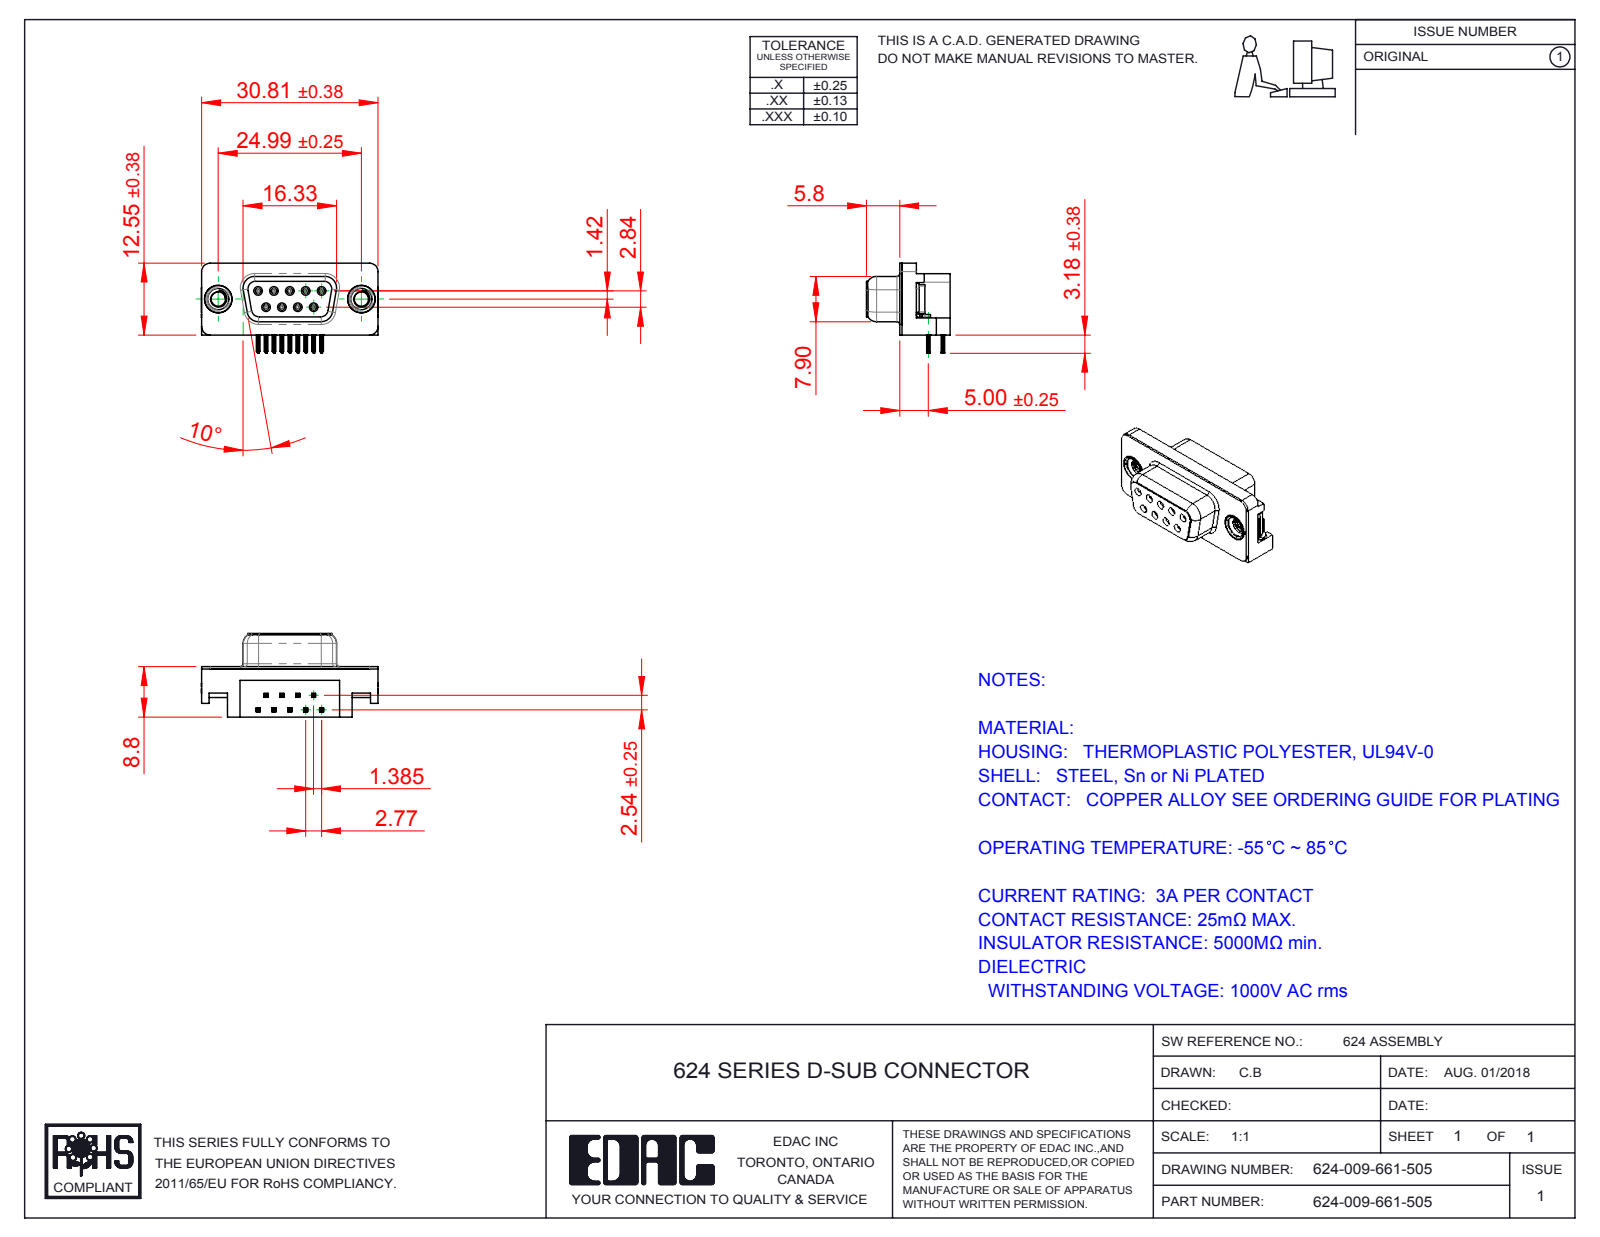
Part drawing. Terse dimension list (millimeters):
name: 624 Shell_9 Socket; 624 Housing_9 Socket; 624-009-661-505; 624 M3 Threaded Rivet (+3 more)
written by: SolidWorks 2016 (CONFIG_CONTROL_DESIGN)
unit: mm
bodies: 15 solids, 1520 faces (642 planar, 410 cylindrical, 468 other)
size: 30.89 × 15.73 × 14.6
volume: 2 932 mm³; area: 4 338 mm²
holes: 9× ⌀0.8, 9× ⌀0.9, 2× ⌀2.5, 2× ⌀4, 2× ⌀4.8, 2× ⌀5
bosses: 9× ⌀1.2, 2× ⌀4.9, 2× ⌀4.75, 2× ⌀3.9
rounds: 72× R0.1, 36× R0.15, 18× R0.35, 18× R1, 9× R0.34, 8× R0.25, 8× R1.35, 7× R1.5
face distances: 0.4, 8.4, 8.8, 2.9, 2.5, 6.2, 5.9, 0.35, 10.69, 10.34
hole spacings: 3.16, 2.77, 5.54, 5.03, 5.04, 8.31, 7.48, 7.49
